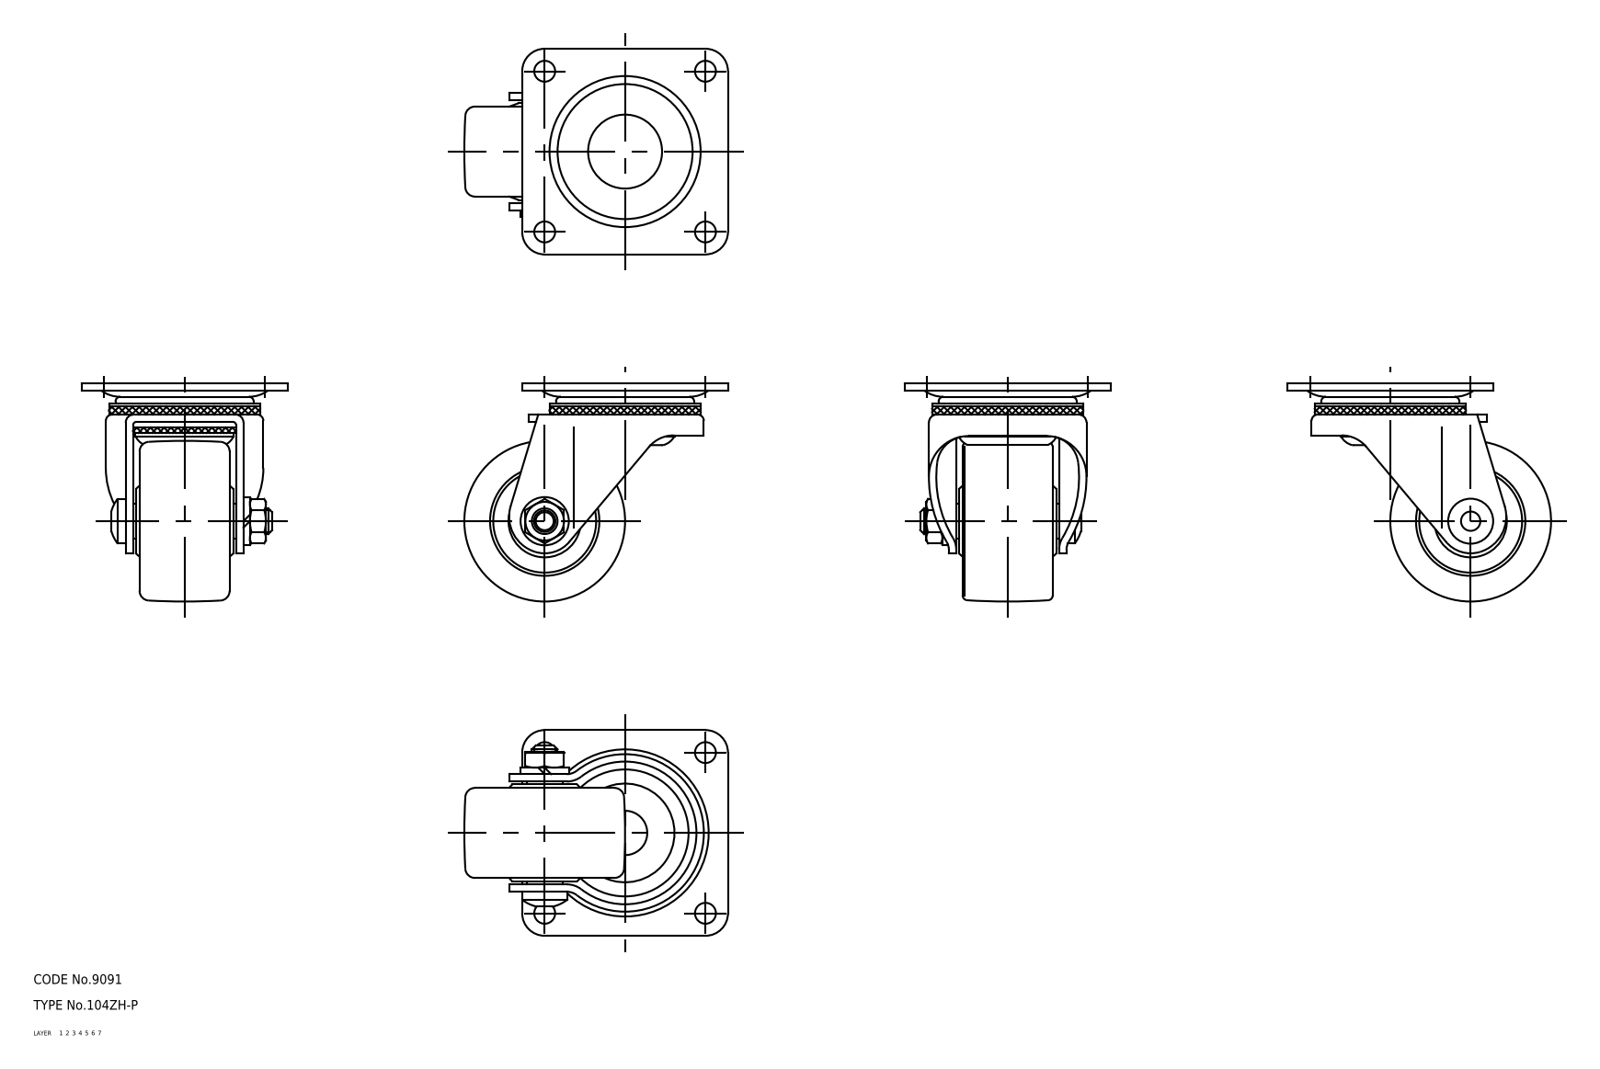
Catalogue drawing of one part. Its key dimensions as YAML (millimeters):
part_name: "wheel; mounting plate; main shaft; axle (+1 more)"
step_written_by: "CADfix (AUTOMOTIVE_DESIGN)"
units: millimeters
bodies: {solids: 5, faces: 195, planar: 0, cylindrical: 0, other: 195}
overall_size: [82, 68, 64]
volume: 94698
surface_area: 33584
